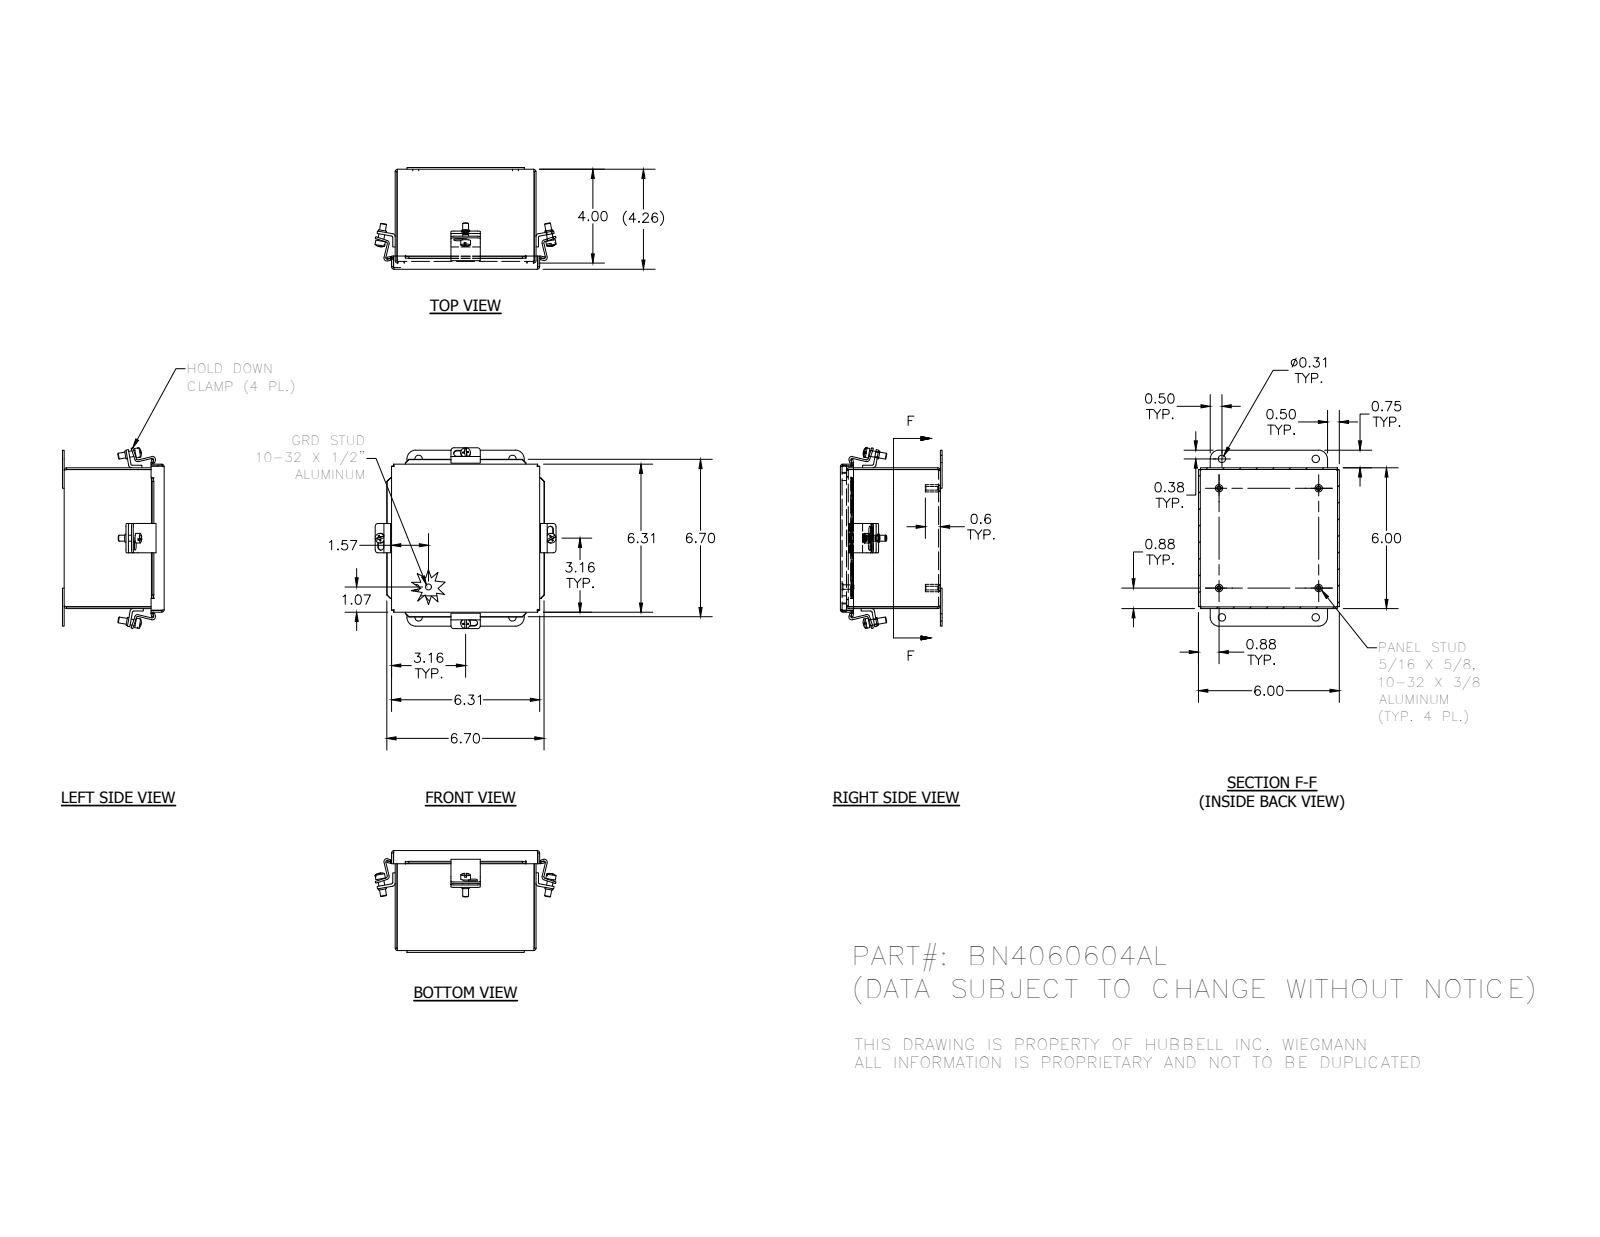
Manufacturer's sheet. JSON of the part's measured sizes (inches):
{"part_name": "38830_1; BN4060604ALBKP_1; 3086_1; BN40606ALLID_1 (+6 more)", "step_written_by": "SolidWorks 2014 (AUTOMOTIVE_DESIGN)", "units": "inches", "bodies": {"solids": 23, "faces": 533, "planar": 295, "cylindrical": 176, "other": 62}, "overall_size": [7.711, 7.706, 4.336], "volume_in3": 19.23, "surface_area_in2": 491.8, "round_holes": [[0.156, 4], [0.196, 4], [0.25, 4], [0.31, 4]], "round_bosses_or_shafts": [[0.25, 5], [0.41, 4], [0.344, 4], [0.313, 4], [0.19, 1]], "partial_cylinders_radius": [[0.031, 16], [0.105, 16], [0.125, 16], [0.063, 12], [0.126, 12], [0.133, 8], [0.375, 4]], "face_to_face_distances": [0.074, 5.926, 4.187, 6, 5.852, 4.261, 4.113, 0.261, 3.926, 0.187], "hole_center_spacings": [1.256, 4.25, 4.31, 5.502, 4, 6.01, 6.75, 6.875]}
